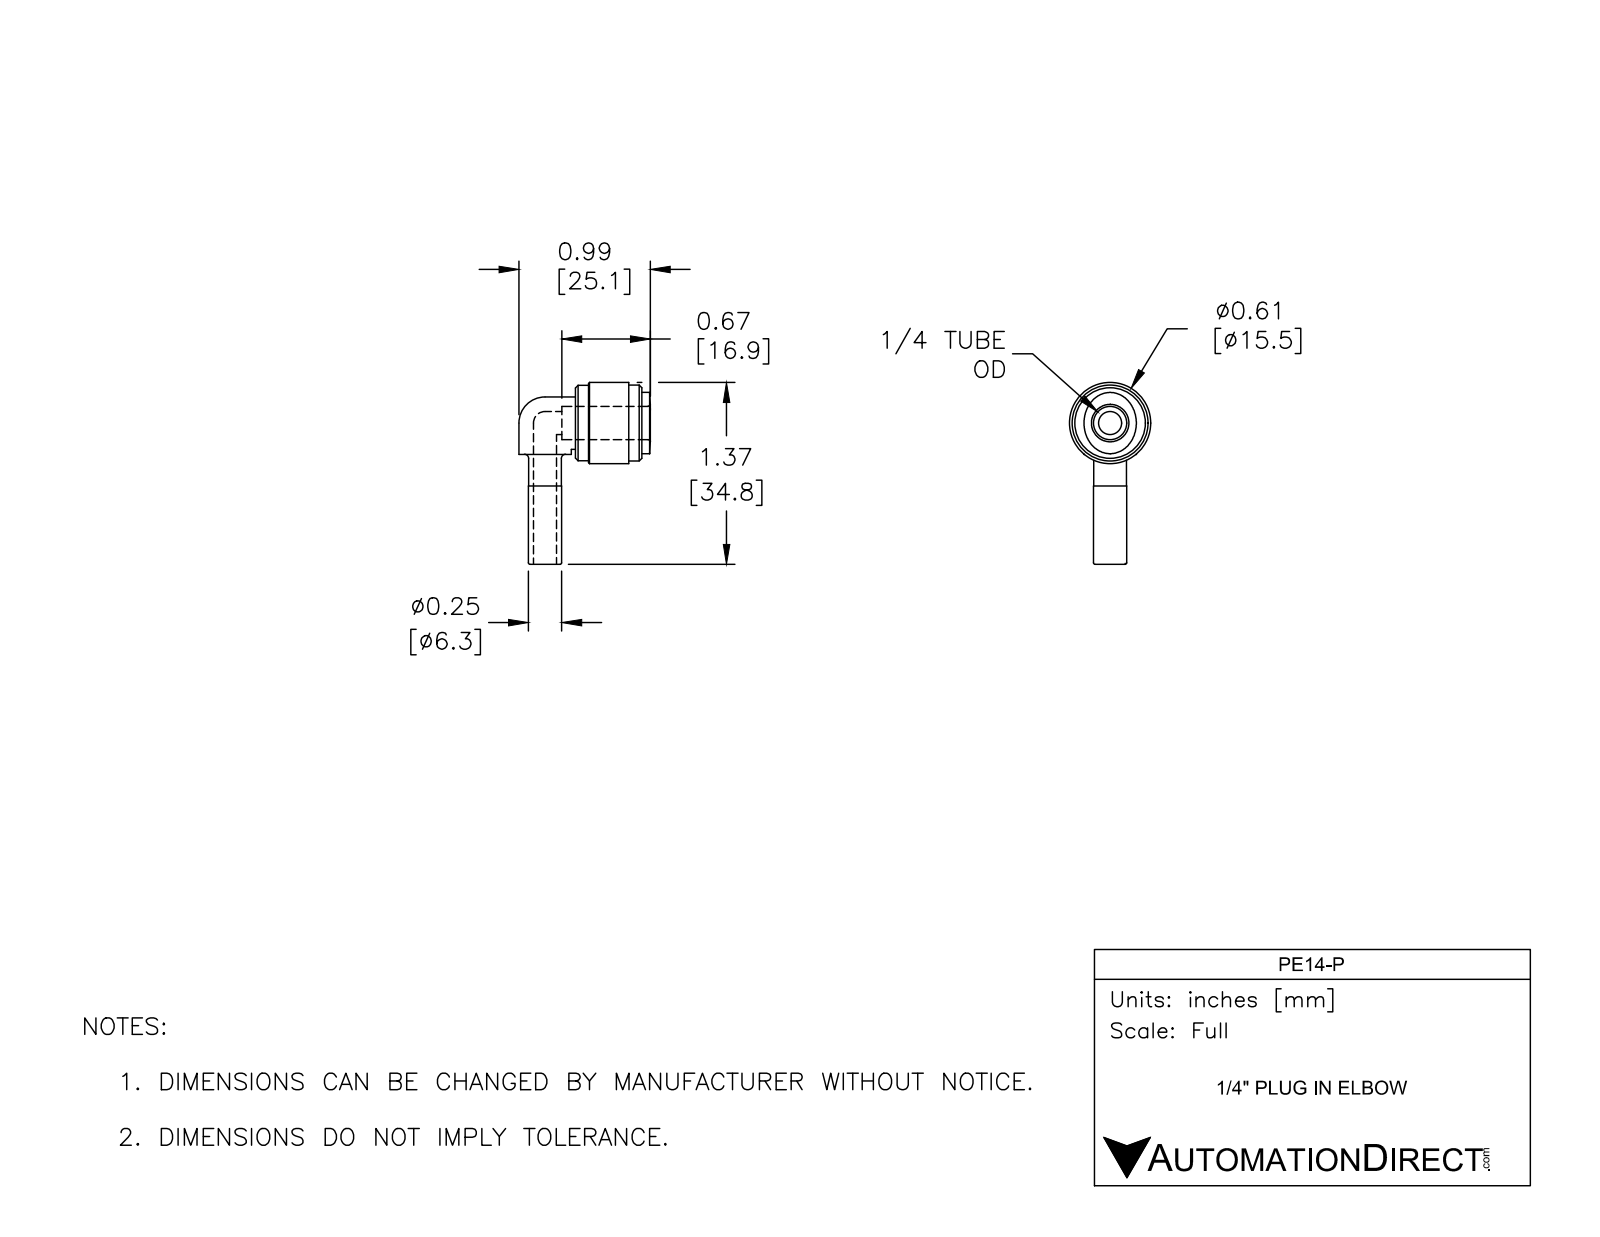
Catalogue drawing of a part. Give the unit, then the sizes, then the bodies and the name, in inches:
Units: inches
Overall size (bounding box): 1.368 × 0.988 × 0.61
Round holes (diameter × count): ⌀0.173 ×2, ⌀0.25 ×1
Round bosses / shafts (diameter × count): ⌀0.394 ×2, ⌀0.61 ×1, ⌀0.571 ×1, ⌀0.567 ×1, ⌀0.25 ×1, ⌀0.246 ×1
Main face-to-face distances: 0.5, 0.098, 0.402, 0.102, 0.504, 0.602, 0.201, 0.303, 0.827, 0.591
Volume: 0.181 in³ · Surface area: 3.833 in²
Bodies: 1 solid, 48 faces (8 planar, 20 cylindrical, 20 other)
Part name (STEP PRODUCT): PE14-P
STEP written by: SolidWorks 2017 (AUTOMOTIVE_DESIGN)
